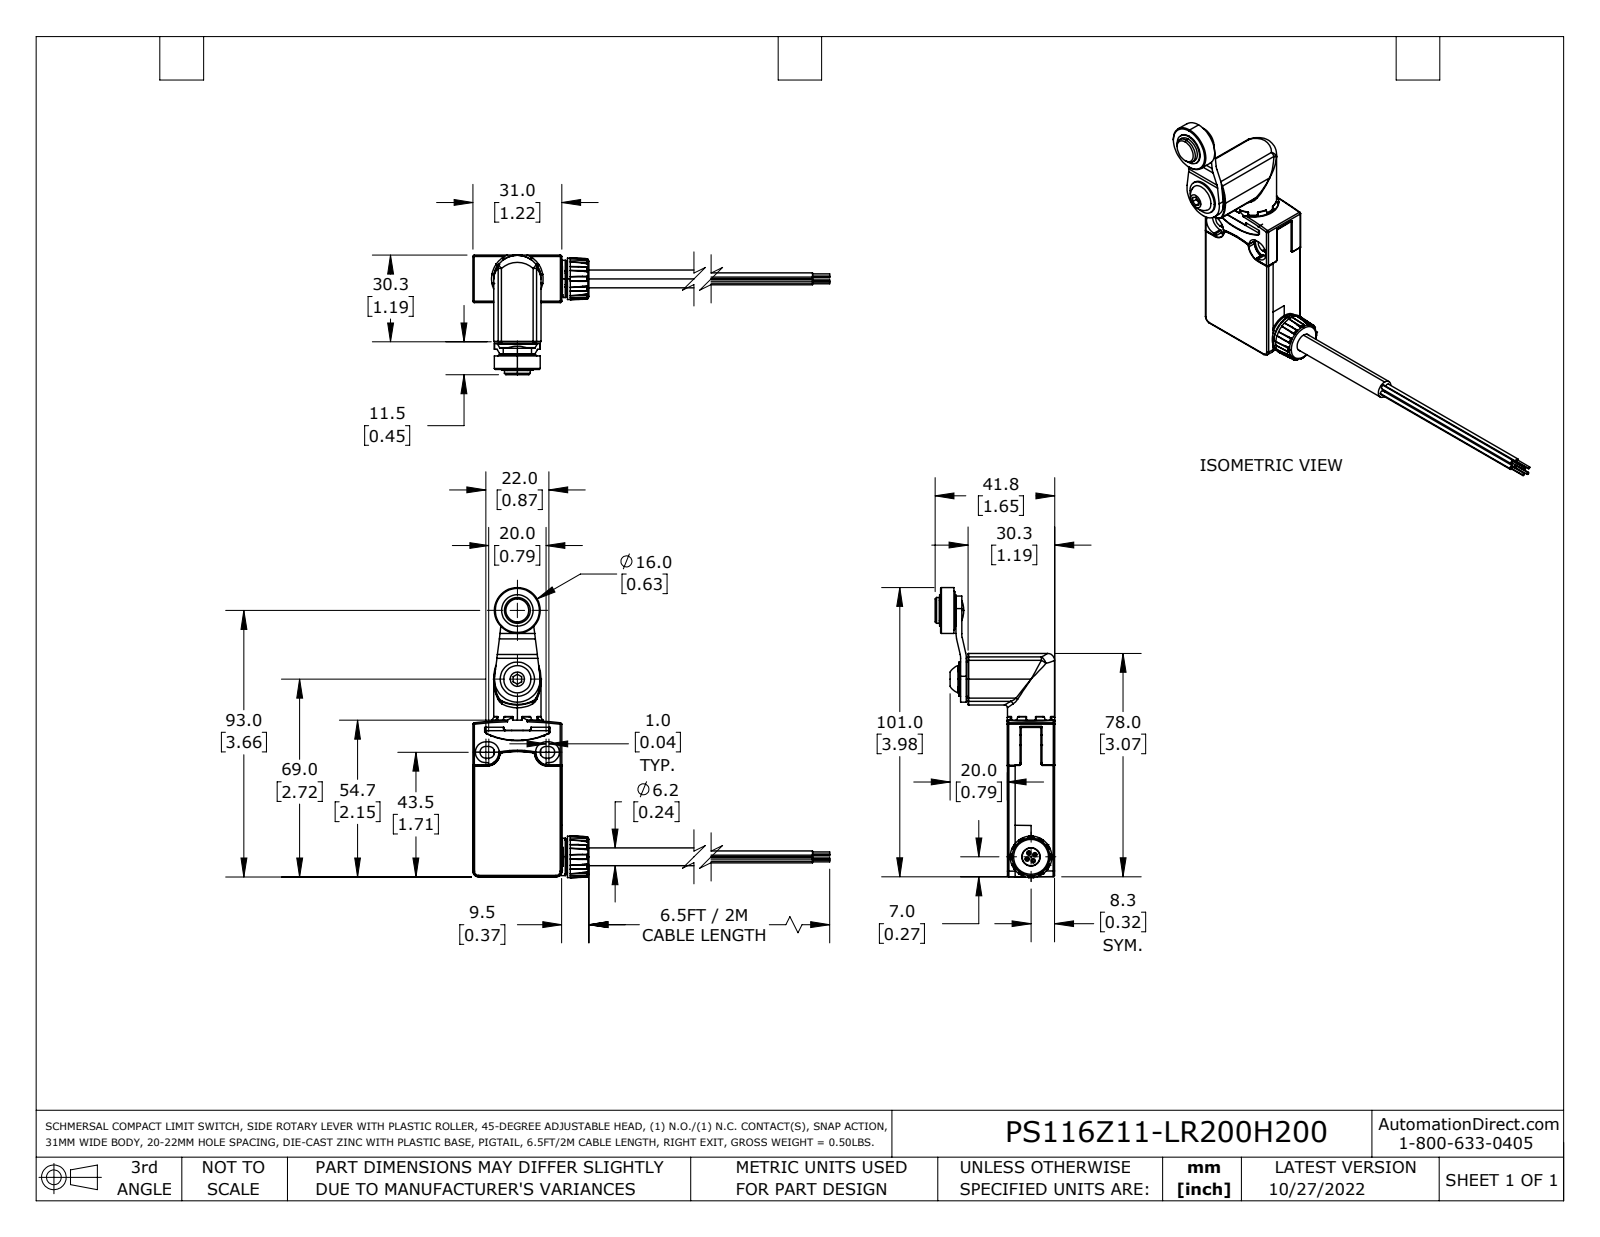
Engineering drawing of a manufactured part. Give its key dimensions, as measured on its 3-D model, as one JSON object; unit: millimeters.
{"part_name": "PS116Z11-LR200H200_Default", "step_written_by": "SolidWorks 2021 (CONFIG_CONTROL_DESIGN)", "units": "millimeters", "bodies": {"solids": 1, "faces": 1082, "planar": 335, "cylindrical": 442, "other": 305}, "overall_size": [150.5, 101.3, 41.8], "volume_mm3": 39800, "surface_area_mm2": 18010, "round_holes": [[12.2, 2], [2, 1], [6.4, 1], [14.5, 1], [14.8, 1]], "round_bosses_or_shafts": [[1.5, 4], [0.8, 4], [13, 2], [16.5, 1], [16, 1], [14.5, 1], [14.4, 1], [13.3, 1]], "partial_cylinders_radius": [[0.2, 134], [0.1, 61], [0.5, 30], [0.4, 10], [1, 8], [0.3, 6], [2, 5], [2.1, 4]], "face_to_face_distances": [16.5, 16.6, 2, 31, 1.6, 3, 16.6, 0.4, 11.5, 7.4], "hole_center_spacings": [41]}
